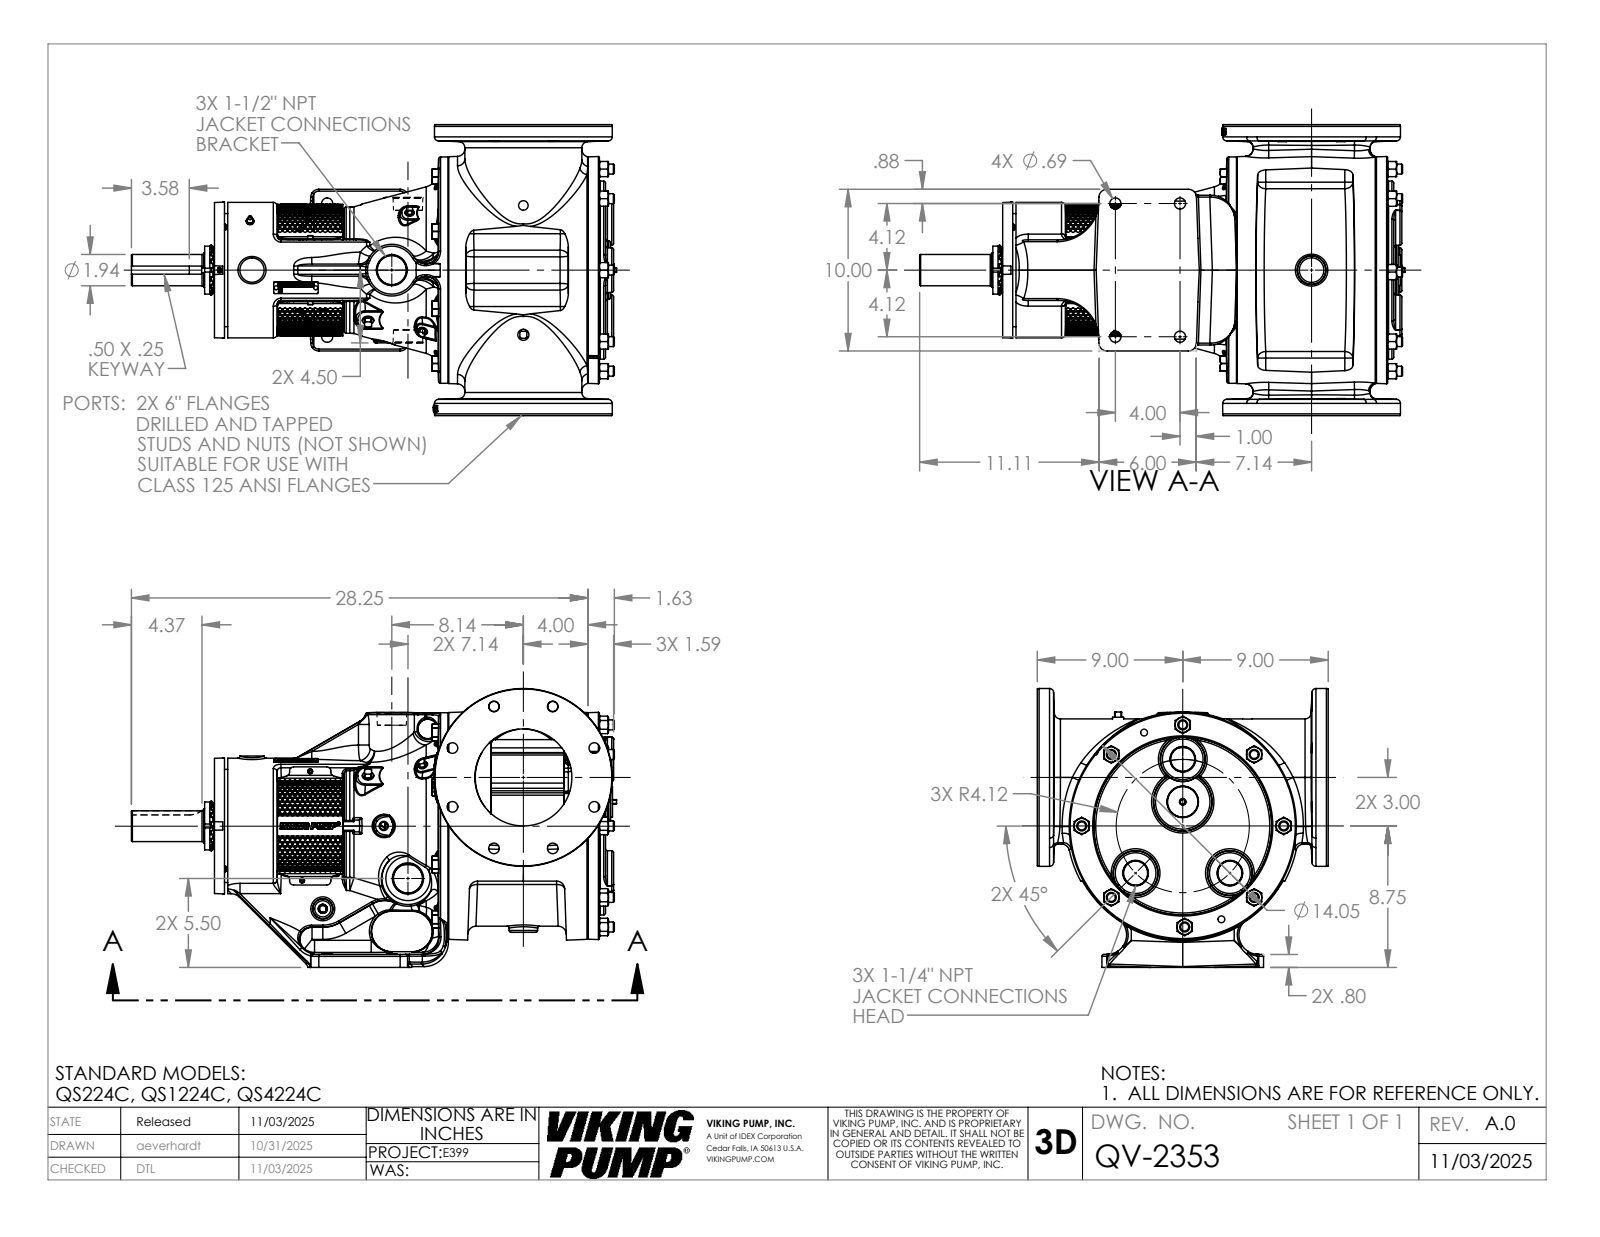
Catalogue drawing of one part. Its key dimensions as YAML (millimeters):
part_name: "QV-2353"
step_written_by: "SolidWorks 2024 (AUTOMOTIVE_DESIGN)"
units: millimeters
bodies: {solids: 1, faces: 4022, planar: 1344, cylindrical: 670, other: 2008}
overall_size: [762.4, 577.6, 438.2]
volume: 43690000
surface_area: 1528000
round_holes:
  - {diameter: 6.8, count: 8}
  - {diameter: 16.7, count: 8}
  - {diameter: 29.4, count: 8}
  - {diameter: 6.4, count: 6}
  - {diameter: 17.5, count: 4}
  - {diameter: 4, count: 2}
  - {diameter: 8, count: 2}
  - {diameter: 10.7, count: 2}
  - {diameter: 11.5, count: 1}
  - {diameter: 54.8, count: 1}
  - {diameter: 55, count: 1}
  - {diameter: 55.4, count: 1}
round_bosses_or_shafts:
  - {diameter: 19.1, count: 8}
  - {diameter: 18.8, count: 8}
  - {diameter: 15.7, count: 8}
  - {diameter: 11.1, count: 3}
  - {diameter: 7.9, count: 3}
  - {diameter: 9.5, count: 2}
  - {diameter: 355.6, count: 1}
  - {diameter: 279.4, count: 1}
partial_cylinders:
  - {radius: 3, count: 54}
  - {radius: 12.7, count: 22}
  - {radius: 19.1, count: 22}
  - {radius: 0.4, count: 18}
  - {radius: 2.3, count: 18}
  - {radius: 1.8, count: 16}
  - {radius: 6.4, count: 10}
  - {radius: 1.5, count: 8}
face_to_face_distances: [457.2, 38.1, 419.1, 9.7, 605, 614.6, 381, 97, 507.9, 517.6]
hole_center_spacings: [95.3, 52.8, 146.9, 68.9, 79.6, 96.2, 137.7, 150.7]
